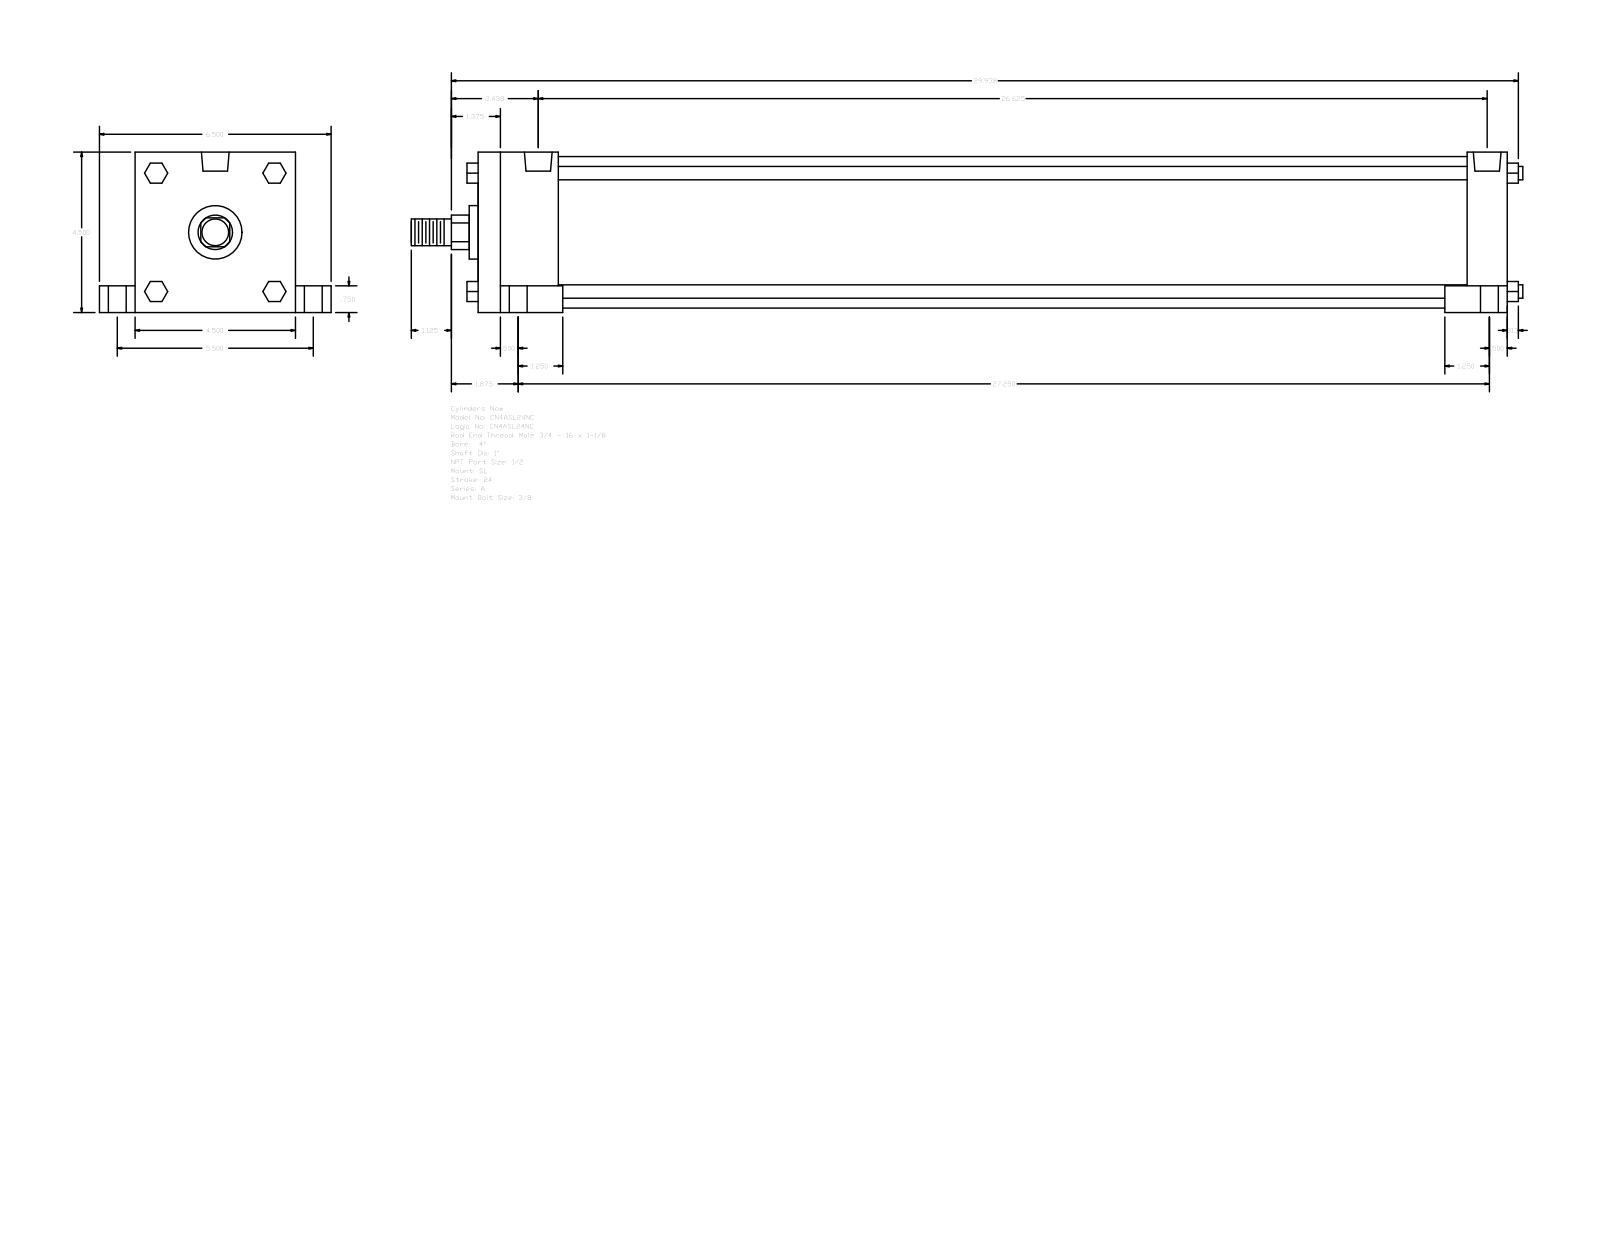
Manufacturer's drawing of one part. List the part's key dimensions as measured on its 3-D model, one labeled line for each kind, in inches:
Part name (STEP PRODUCT): A_SL__0400_1
STEP written by: GSSL Pune (CONFIG_CONTROL_DESIGN)
Units: inches
Bodies: 0 solids, 150 faces (114 planar, 36 cylindrical, 0 other)
Overall size (bounding box): 31.187 × 6.5 × 4.5
Round holes (diameter × count): ⌀0.344 ×4, ⌀0.5 ×4, ⌀0.75 ×4, ⌀0.778 ×2
Round bosses / shafts (diameter × count): ⌀0.375 ×4, ⌀4.25 ×1, ⌀1.5 ×1, ⌀1 ×1, ⌀0.75 ×1
Partial cylindrical surfaces — rounded edges, fillets, slot ends (radius × count): R0.484 ×1
Main face-to-face distances: 4.5, 28.875, 2.25, 26.625, 27.75, 25.5, 1.125, 0.75, 1, 5.5
Hole centre spacings: 0.125, 2.751, 2.756, 2.807, 2.835, 5.5, 26.375, 26.5
